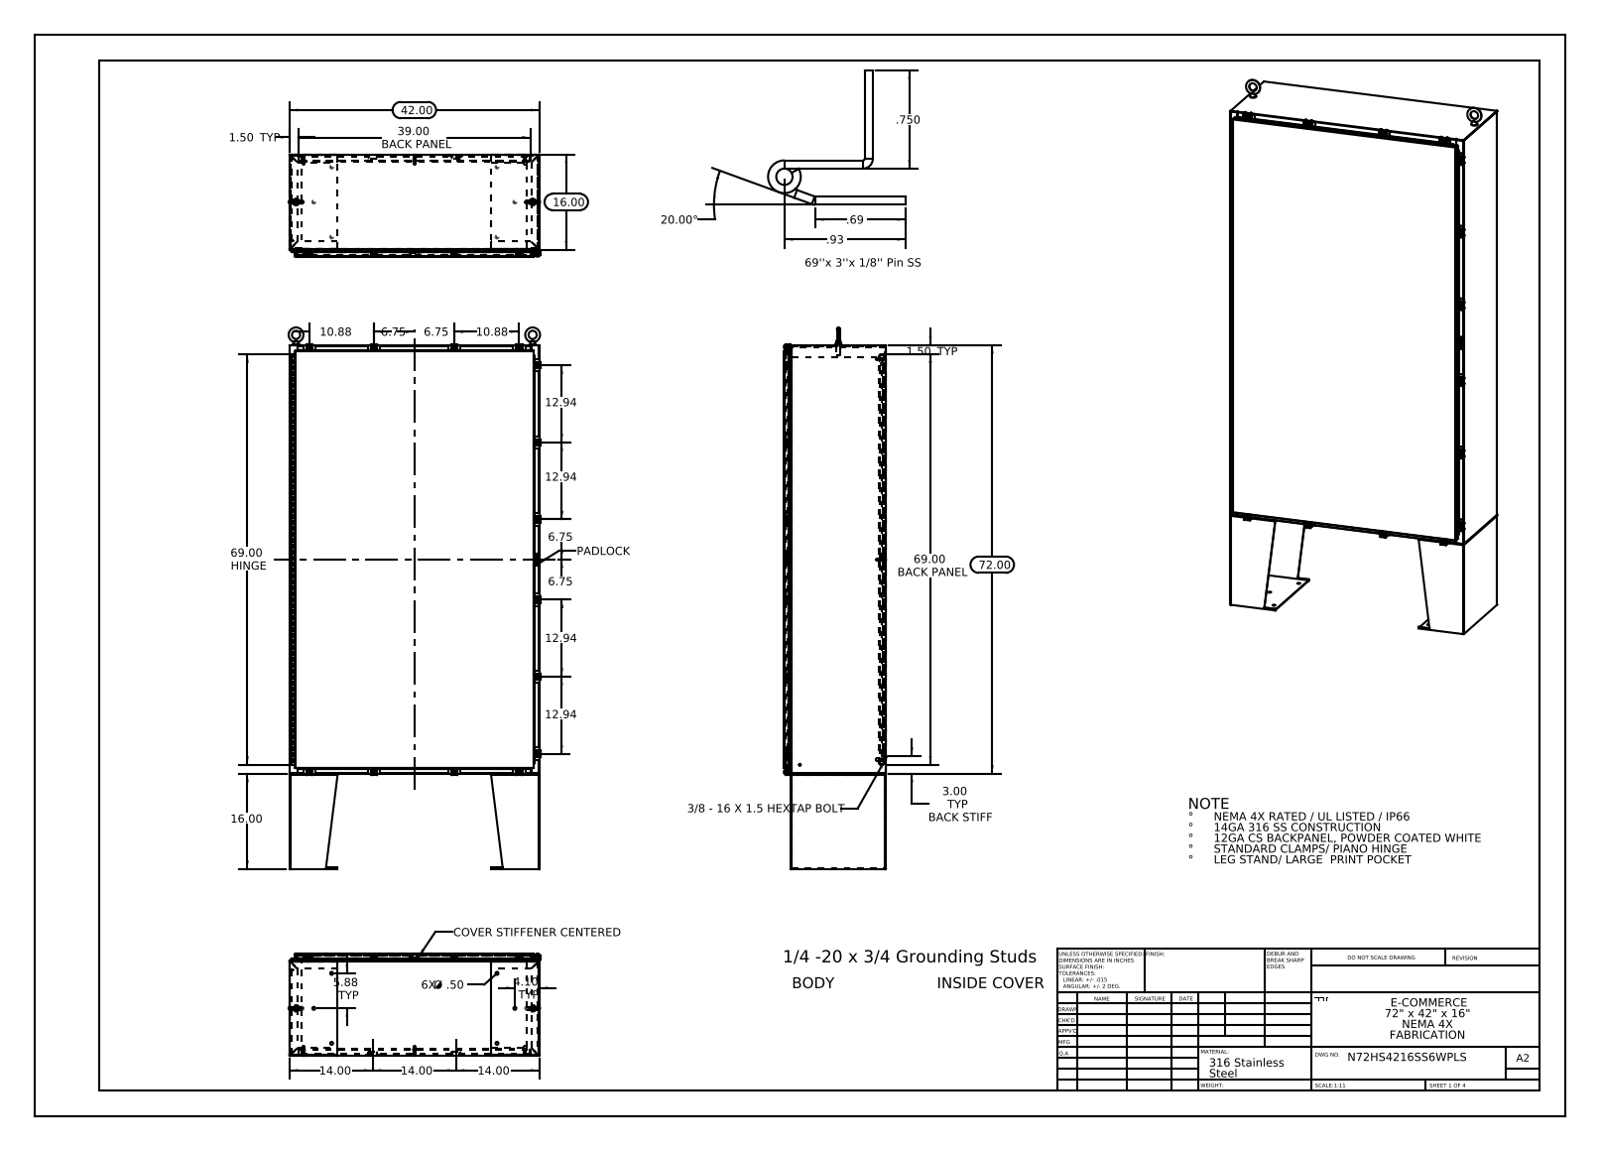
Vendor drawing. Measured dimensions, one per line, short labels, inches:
name: 10_30 CD Stud; N72HS4216SSWPLS Door Stiffener; N72HS4216SSWPLS Body; N72HS4216SSWPLS Hinge Cover Side (+8 more)
written by: SolidWorks 2013 (CONFIG_CONTROL_DESIGN)
unit: in
bodies: 108 solids, 4313 faces (2196 planar, 1809 cylindrical, 308 other)
size: 91 × 42.346 × 17.201
volume: 1 282 in³; area: 31 036 in²
holes: 14× ⌀0.213, 14× ⌀0.26, 14× ⌀0.5, 8× ⌀0.25, 4× ⌀0.75, 2× ⌀0.125, 1× ⌀0.125
bosses: 15× ⌀0.25, 14× ⌀0.5, 14× ⌀0.399, 10× ⌀0.625, 8× ⌀0.375, 8× ⌀0.33, 8× ⌀0.157, 8× ⌀0.14
rounds: 62× R0.06, 39× R0.013, 33× R0.088, 28× R0.12, 28× R0.141, 25× R0.05, 24× R0.145, 20× R0.08
face distances: 0.075, 17.126, 0.104, 17.051, 1.075, 17.201, 16.126, 1, 16.051, 1.179
hole spacings: 7.069, 2.225, 8.393, 31.348, 33.625, 34.289, 35.74, 38.439
